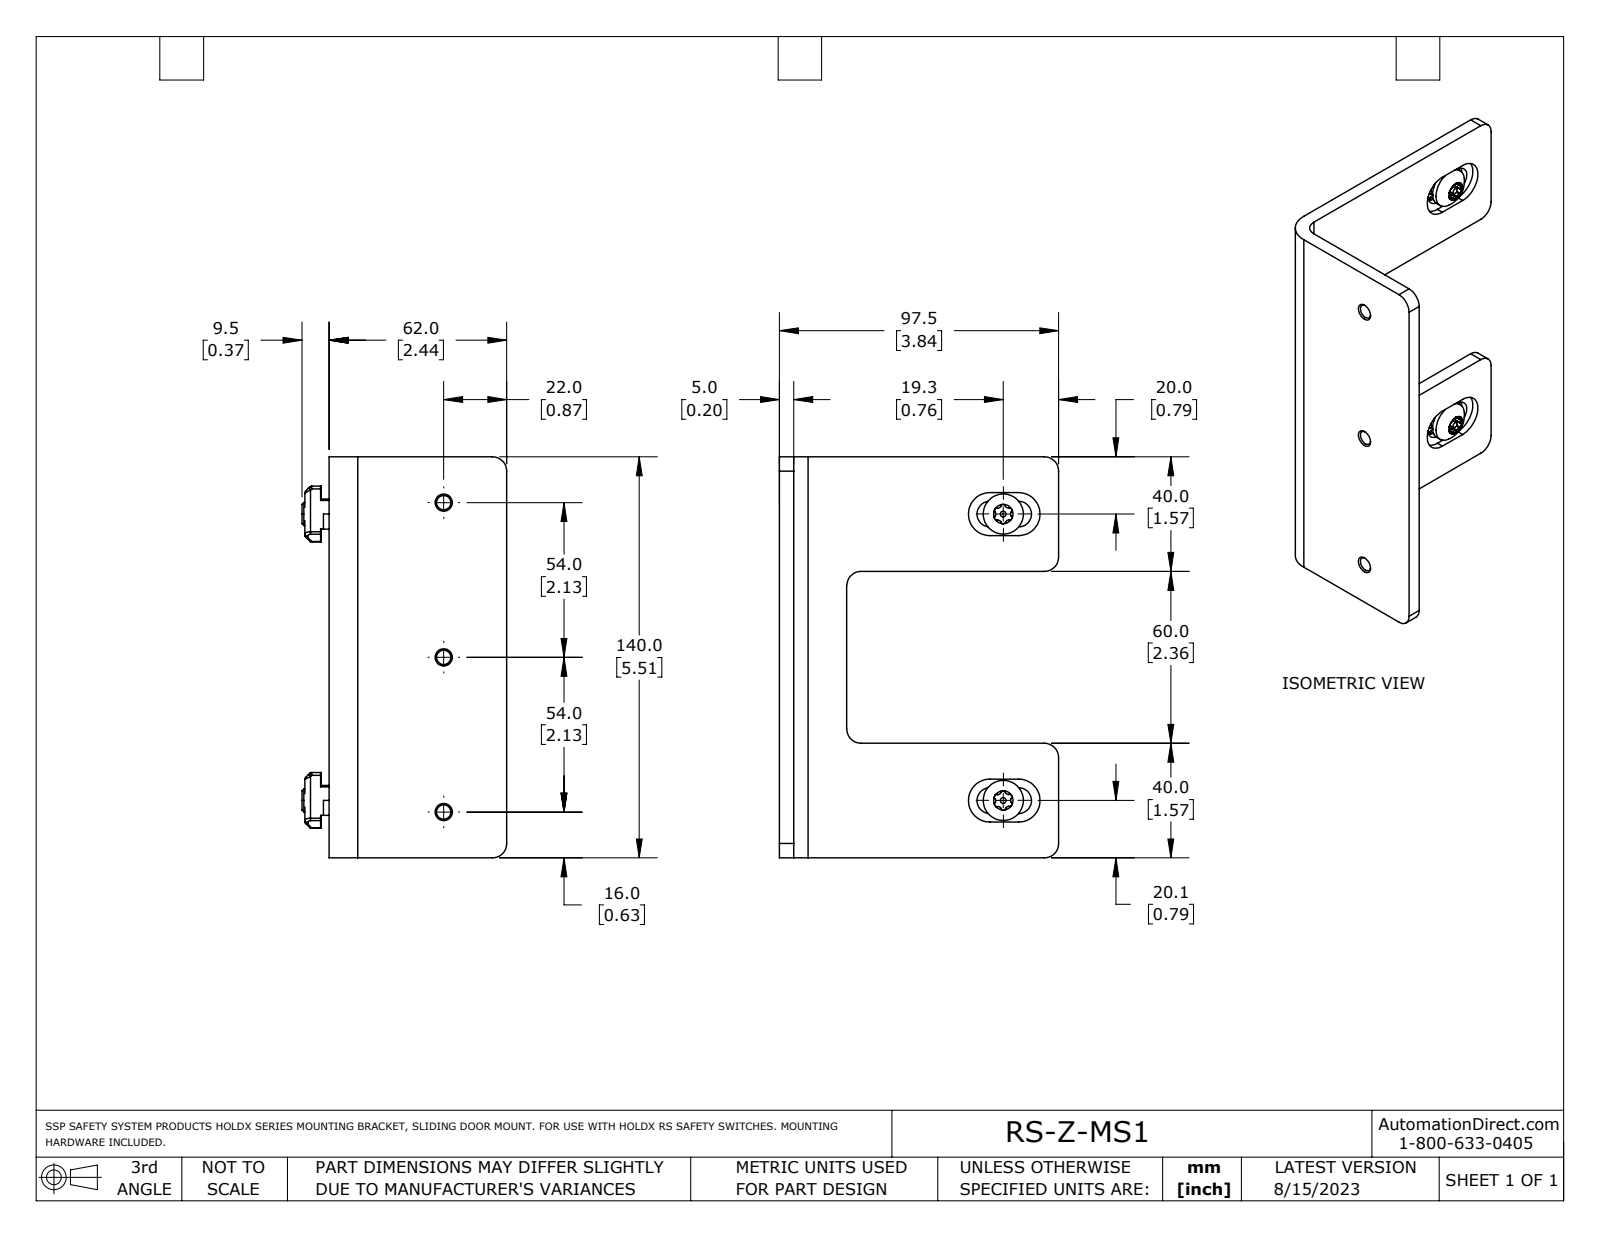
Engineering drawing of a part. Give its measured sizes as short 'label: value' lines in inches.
name: RS-Z-MS1_REV1
written by: SolidWorks 2021 (AUTOMOTIVE_DESIGN)
unit: in
bodies: 5 solids, 299 faces (118 planar, 149 cylindrical, 32 other)
size: 5.512 × 3.839 × 2.815
volume: 5.185 in³; area: 62.53 in²
holes: 3× ⌀0.197, 2× ⌀0.266, 2× ⌀0.266
bosses: 2× ⌀0.551, 2× ⌀0.315, 2× ⌀0.079
rounds: 48× R0.011, 30× R0.039, 24× R0.056, 9× R0.197, 4× R0.02, 4× R0.079, 4× R0.177, 4× R0.295
face distances: 0.197, 0.098, 3.937, 5.512, 2.441, 2.244, 1.575, 2.343, 2.362, 3.839
hole spacings: 2.126, 3.936, 4.252
